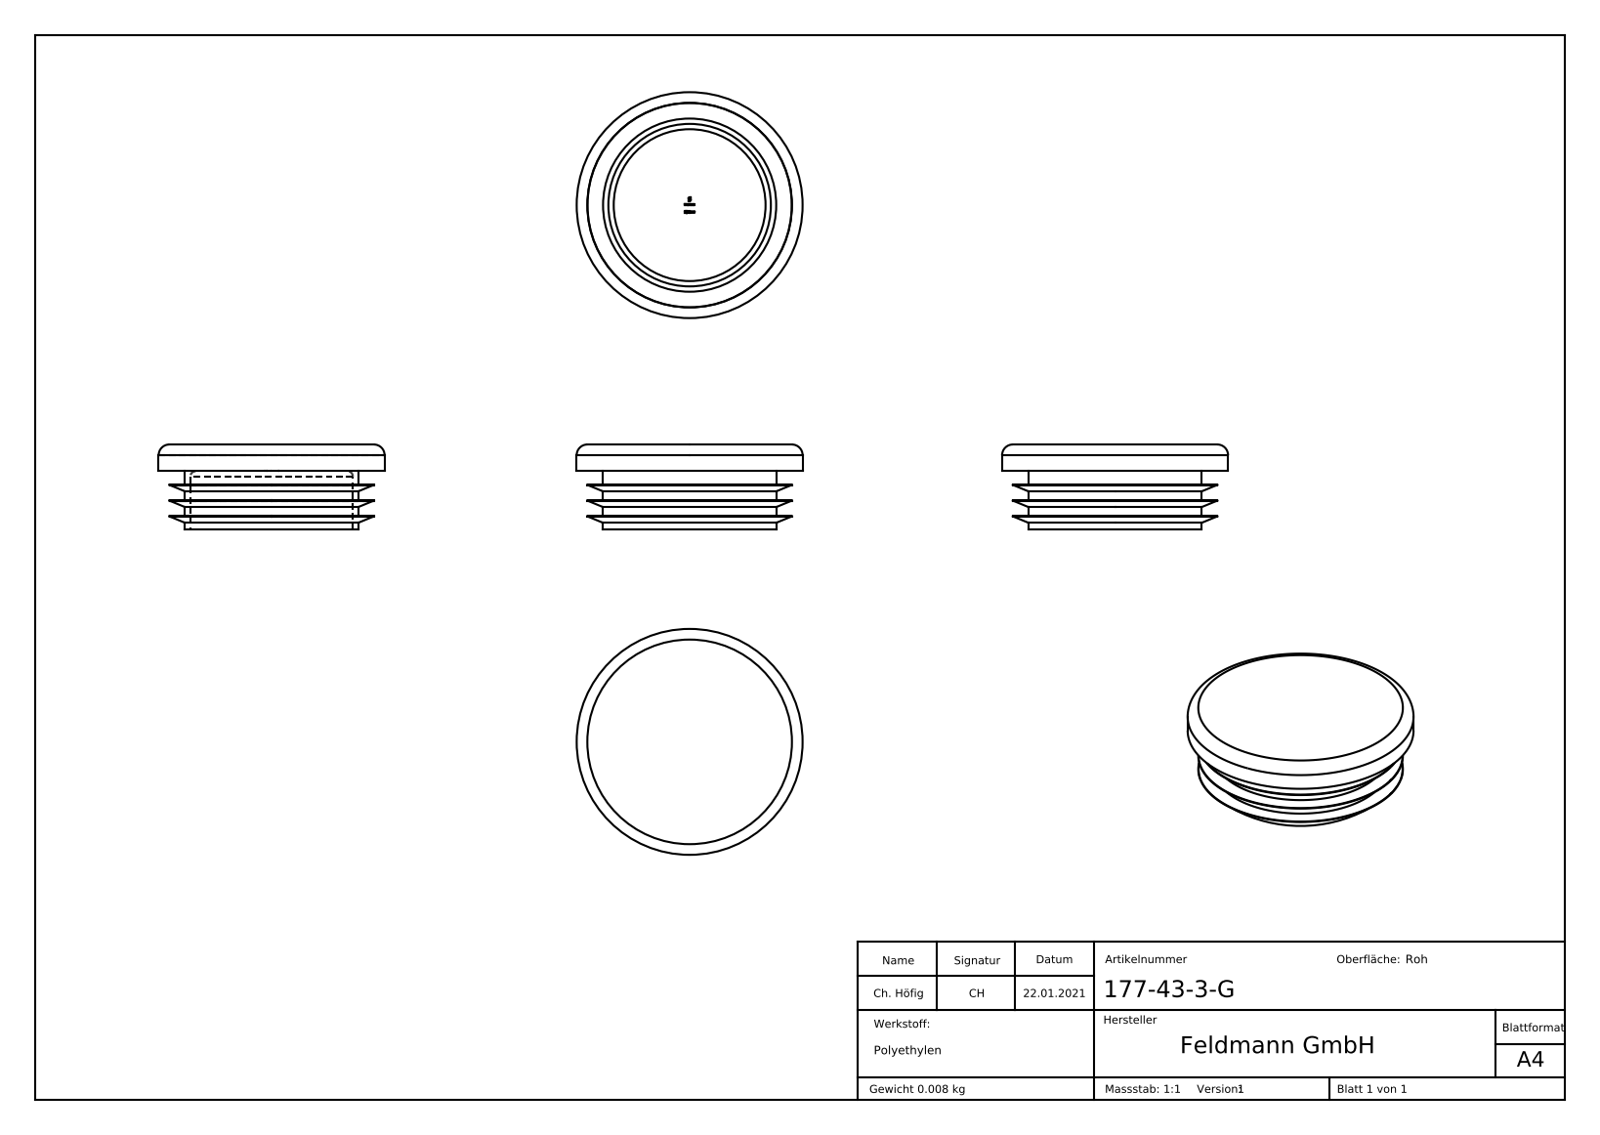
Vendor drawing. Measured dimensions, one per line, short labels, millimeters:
name: 177-43-3-G
written by: SolidWorks 2018 (CONFIG_CONTROL_DESIGN)
unit: mm
bodies: 1 solid, 290 faces (157 planar, 12 cylindrical, 121 other)
size: 42.4 × 42.4 × 16
volume: 8 722 mm³; area: 7 185 mm²
holes: 1× ⌀30.5
bosses: 1× ⌀42.4, 1× ⌀32.5
face distances: 5, 2.95, 2.5, 7.5, 5.45, 10.45, 5.9, 8.4, 13.4, 2.6
